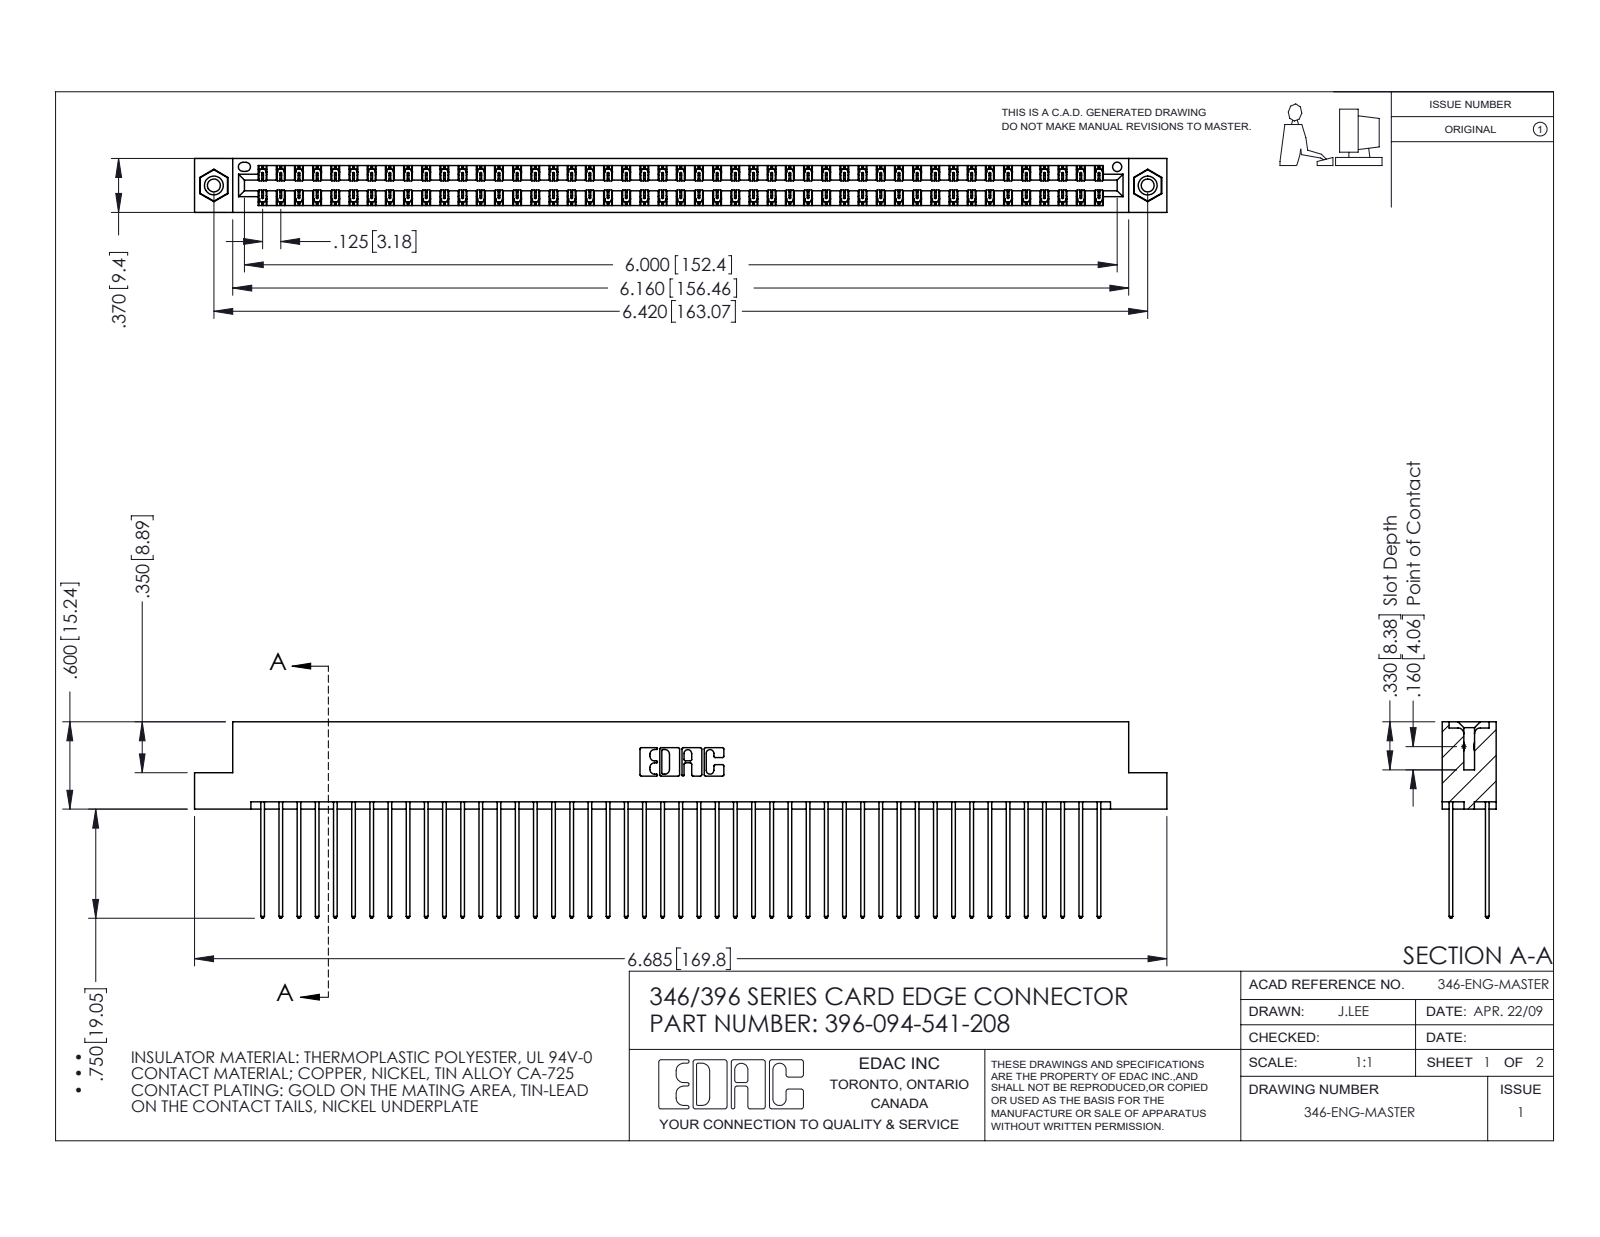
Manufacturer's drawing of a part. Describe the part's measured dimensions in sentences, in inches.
The part is named "346 Part_Flush Mounting Lugs - 0.156 Dia-TI; 345-250-001_345-250-003-102; 396-094-541-208; 345-292-001_345-293-141". Its 3-D file was written by "SolidWorks 2016 (CONFIG_CONTROL_DESIGN)". It is 97 solids with 5070 faces: 3398 planar, 1656 cylindrical and 16 other. Overall it measures 6.685 by 1.35 by 0.37 inches. Its volume is 1.045 cubic inches and its surface area 40.66 square inches. Round holes: 2 of diameter 0.089, 2 of diameter 0.125, 2 of diameter 0.156, 1 of diameter 0.064. Round bosses or shafts: 2 of diameter 0.155. Partial cylindrical surfaces (rounded edges, fillets, slot ends): 141 of radius 0.006, 94 of radius 0.01, 22 of radius 0.01, 6 of radius 0.007, 6 of radius 0.031, 3 of radius 0.026, 2 of radius 0.014, 2 of radius 0.022. The main face-to-face distances are 0.048, 0.322, 0.25, 0.072, 0.298, 0.025, 0.37, 0.275, 0.225, 0.148. The hole center spacings are 0.246, 6.211, 6.42.
